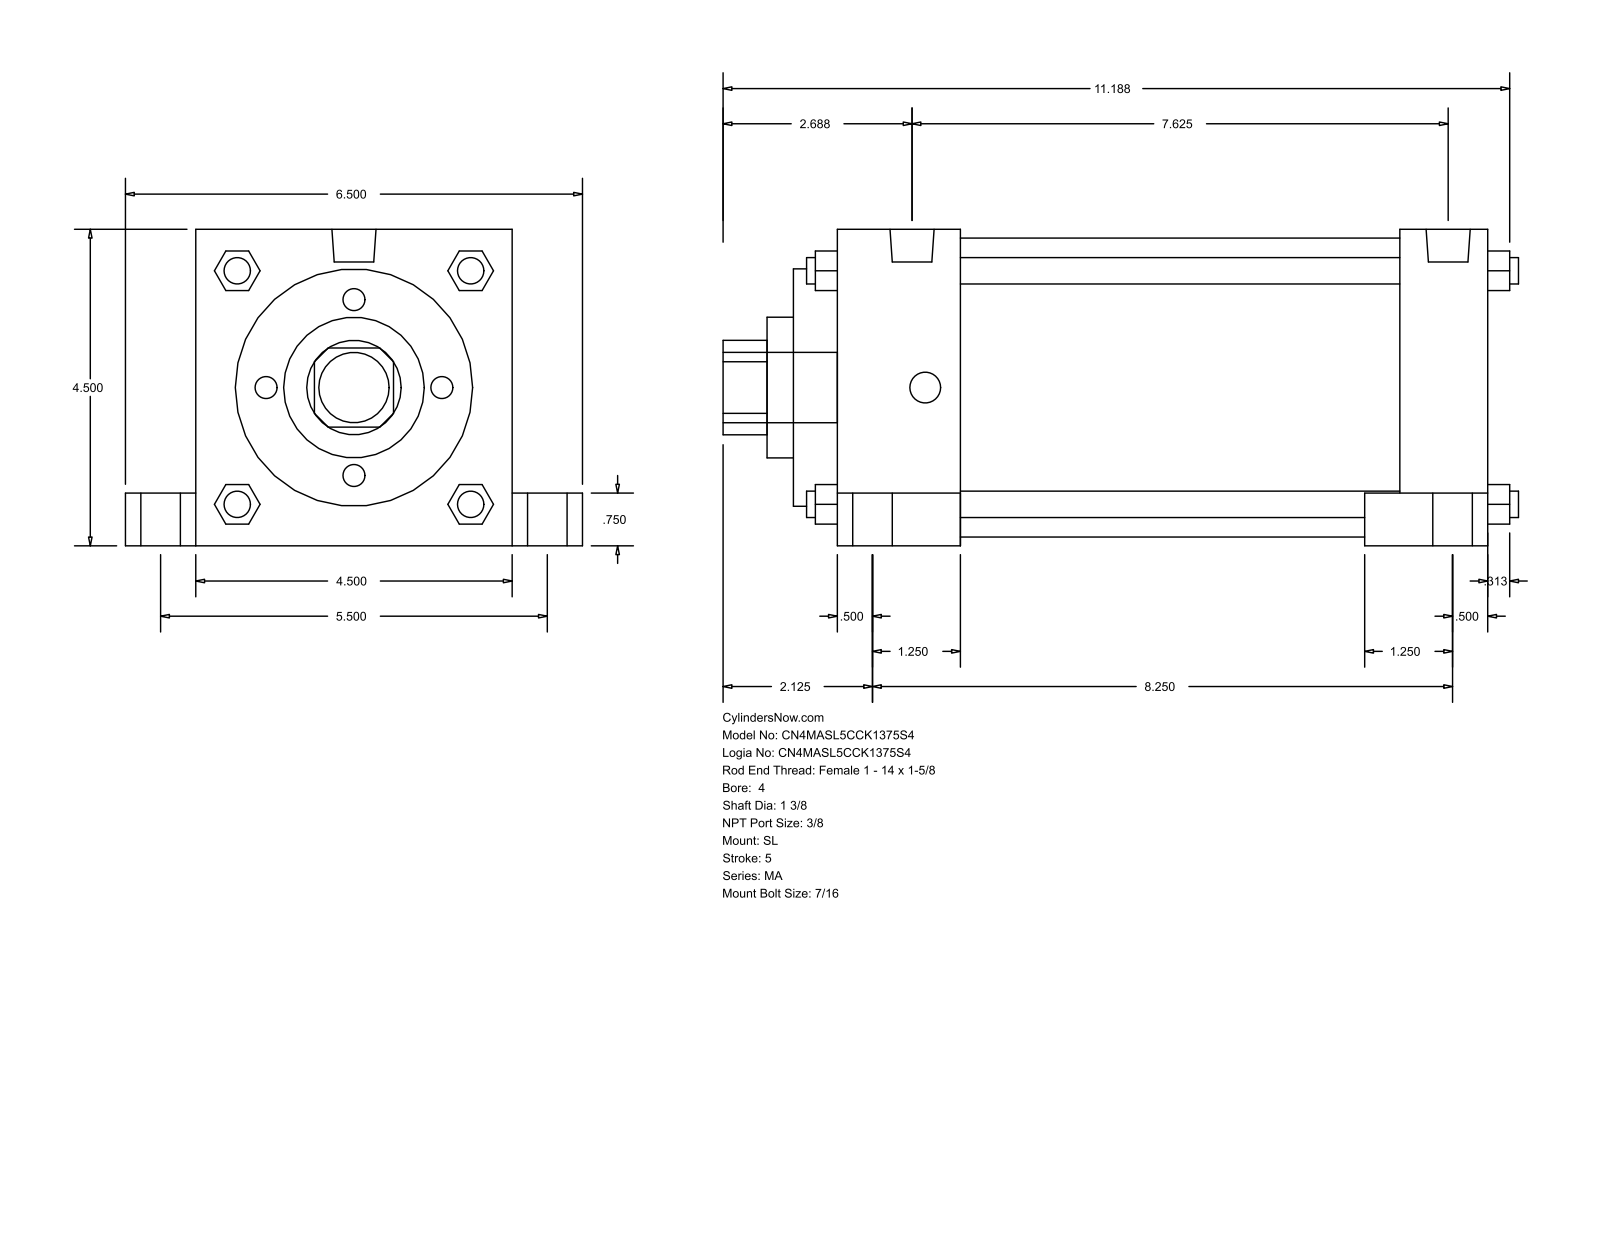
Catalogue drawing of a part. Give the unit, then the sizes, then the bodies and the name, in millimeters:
Units: millimetres
Overall size (bounding box): 287.34 × 165.1 × 114.3
Round holes (diameter × count): ⌀34.92 ×1, ⌀50.8 ×1, ⌀85.72 ×1, ⌀107.95 ×1
Round bosses / shafts (diameter × count): ⌀20.64 ×4, ⌀14.29 ×4, ⌀11.11 ×4, ⌀9.53 ×4, ⌀15.93 ×2, ⌀25.4 ×1
Partial cylindrical surfaces — rounded edges, fillets, slot ends (radius × count): R17.06 ×1
Main face-to-face distances: 114.3, 234.96, 158.75, 15.87, 250.83, 60.32, 44.45, 190.51, 219.07, 203.2
Bodies: 0 solids, 150 faces (113 planar, 37 cylindrical, 0 other)
Part name (STEP PRODUCT): MA_SL__0400_1.375
STEP written by: GSSL Pune (CONFIG_CONTROL_DESIGN)
